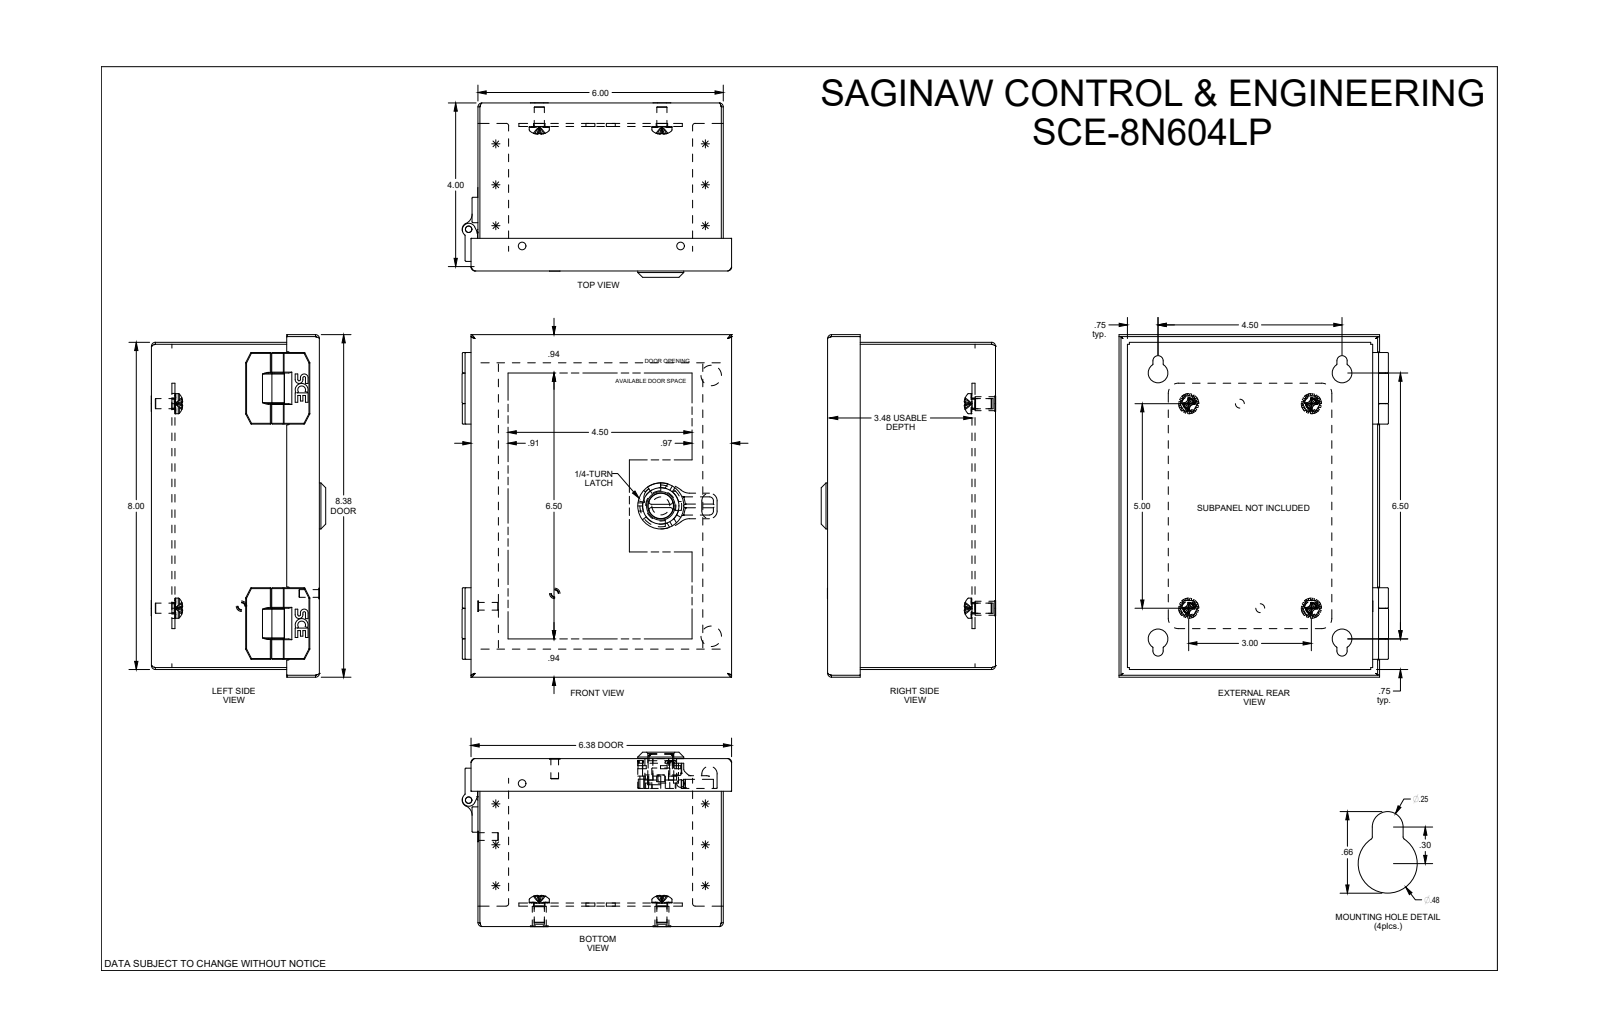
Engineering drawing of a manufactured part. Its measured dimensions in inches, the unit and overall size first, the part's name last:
Units: inches
Overall size (bounding box): 8.375 × 6.593 × 4.267
Round holes (diameter × count): ⌀0.25 ×4, ⌀0.281 ×4, ⌀0.343 ×4, ⌀0.48 ×4, ⌀0.218 ×2, ⌀0.329 ×2, ⌀0.158 ×1, ⌀0.187 ×1, ⌀0.193 ×1, ⌀0.44 ×1, ⌀0.635 ×1, ⌀0.891 ×1
Round bosses / shafts (diameter × count): ⌀0.341 ×4, ⌀0.237 ×4, ⌀0.16 ×4, ⌀0.337 ×2, ⌀0.323 ×2, ⌀0.248 ×2, ⌀1.125 ×1, ⌀0.74 ×1
Partial cylindrical surfaces — rounded edges, fillets, slot ends (radius × count): R0.02 ×95, R0.06 ×25, R0.015 ×16, R0.01 ×13, R0.055 ×6, R0.25 ×6, R0.125 ×4, R0.188 ×3
Main face-to-face distances: 0.06, 4.047, 5.94, 7.94, 3.987, 4.107, 6, 5.88, 0.5, 0.44
Hole centre spacings: 1.061, 3.824, 5.799, 6.865, 1.25, 1.75, 2.136, 2.5
Volume: 18.1 in³ · Surface area: 575.3 in²
Bodies: 21 solids, 737 faces (268 planar, 308 cylindrical, 161 other)
Part name (STEP PRODUCT): SCE-8N604LP_REV2
STEP written by: SolidWorks 2021 (AUTOMOTIVE_DESIGN)
